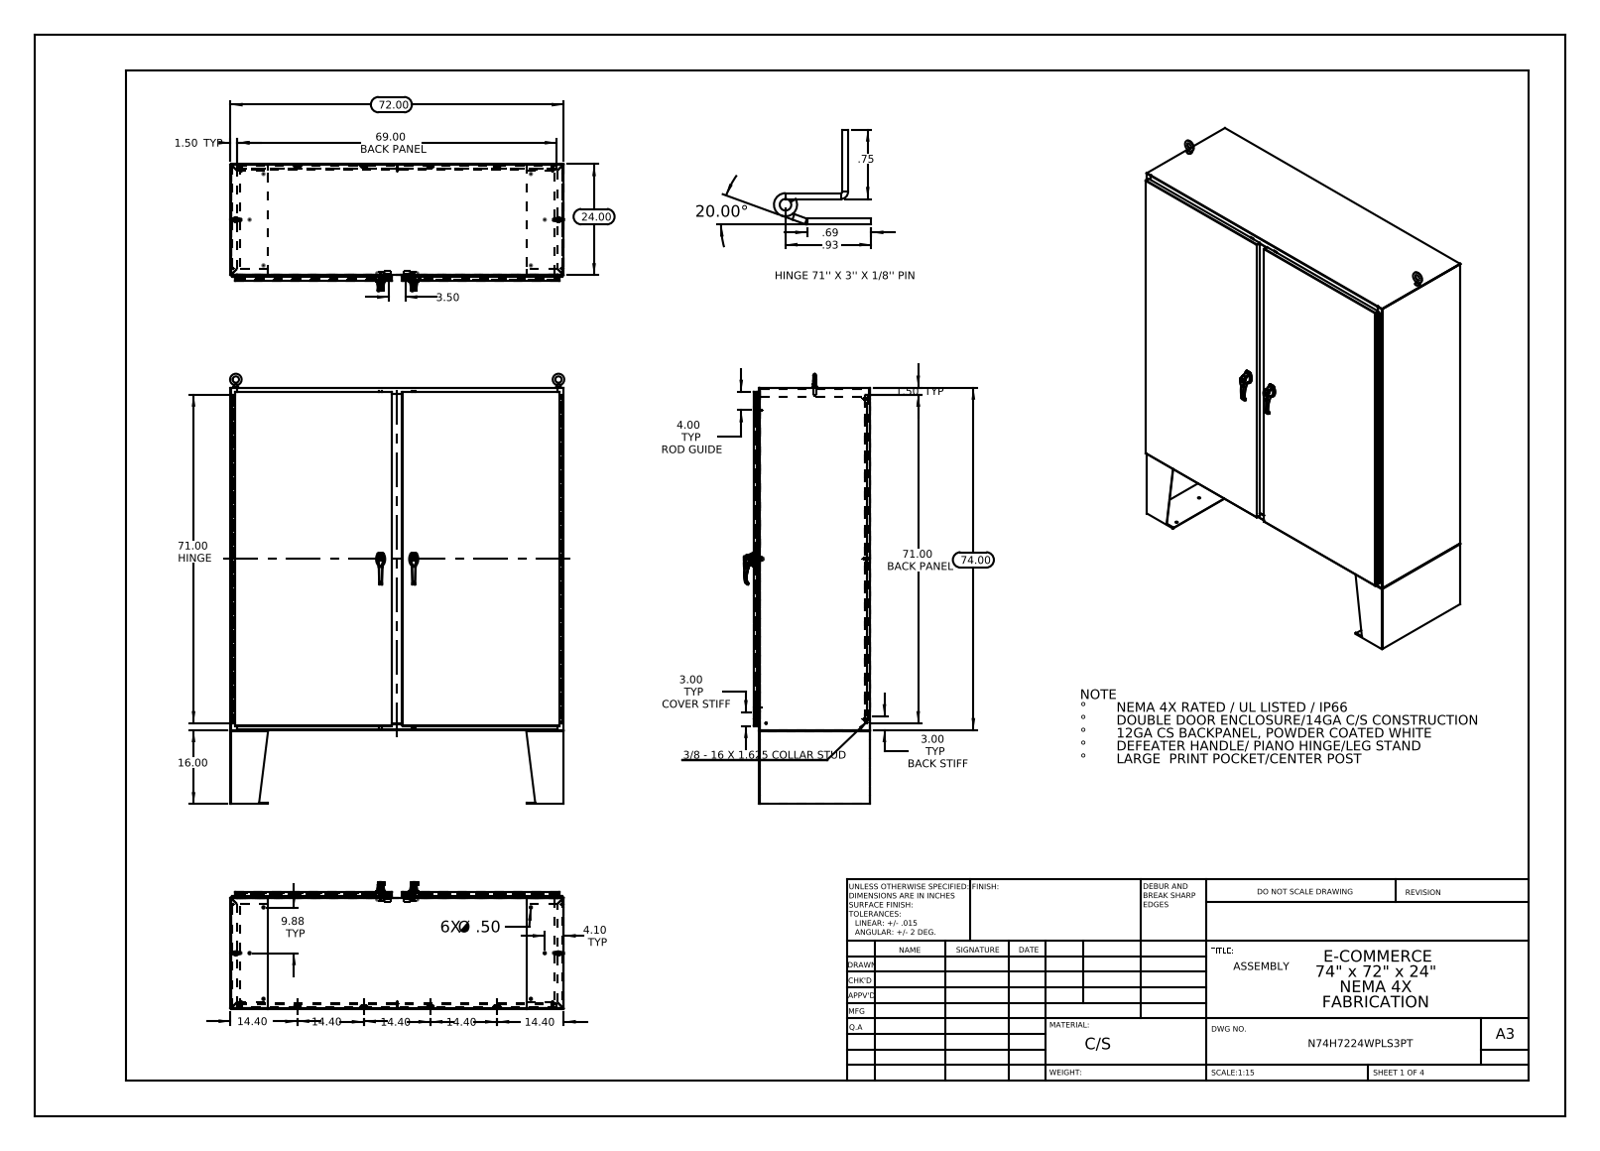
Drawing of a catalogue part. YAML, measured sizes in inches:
part_name: "N74H7224SSWPLS3PT Defeater Handle Stiffener_DD; N74H7224SSWPLS3PT Bottom; N74H7224SSWPLS3PT Right Cover; NMP-SS-RODGUIDES_unfolded_DefaultSM-FLAT-PATTERN (+8 more)"
step_written_by: "SolidWorks 2013 (CONFIG_CONTROL_DESIGN)"
units: inches
bodies: {solids: 83, faces: 7630, planar: 3104, cylindrical: 3066, other: 1460}
overall_size: [93, 72.226, 27.307]
volume: 2272
surface_area: 55376
round_holes:
  - {diameter: 0.25, count: 20}
  - {diameter: 0.5, count: 14}
  - {diameter: 0.138, count: 6}
  - {diameter: 0.161, count: 6}
  - {diameter: 0.079, count: 4}
  - {diameter: 0.313, count: 4}
  - {diameter: 0.437, count: 4}
  - {diameter: 0.75, count: 4}
  - {diameter: 0.125, count: 2}
  - {diameter: 0.125, count: 2}
  - {diameter: 0.197, count: 2}
  - {diameter: 0.203, count: 2}
round_bosses_or_shafts:
  - {diameter: 0.157, count: 12}
  - {diameter: 0.14, count: 12}
  - {diameter: 0.625, count: 10}
  - {diameter: 0.375, count: 8}
  - {diameter: 0.33, count: 8}
  - {diameter: 0.315, count: 5}
  - {diameter: 0.236, count: 5}
  - {diameter: 1.181, count: 2}
partial_cylinders:
  - {radius: 0.118, count: 72}
  - {radius: 0.006, count: 66}
  - {radius: 0.013, count: 50}
  - {radius: 0.088, count: 42}
  - {radius: 0.039, count: 28}
  - {radius: 0.028, count: 24}
  - {radius: 0.008, count: 12}
  - {radius: 0.02, count: 12}
face_to_face_distances: [0.075, 25.126, 0.104, 25.051, 1.075, 25.201, 1, 24.051, 24.126, 1.179]
hole_center_spacings: [7.152, 30.364, 0.295, 0.625, 0.841, 1.313, 1.561, 7.156]
